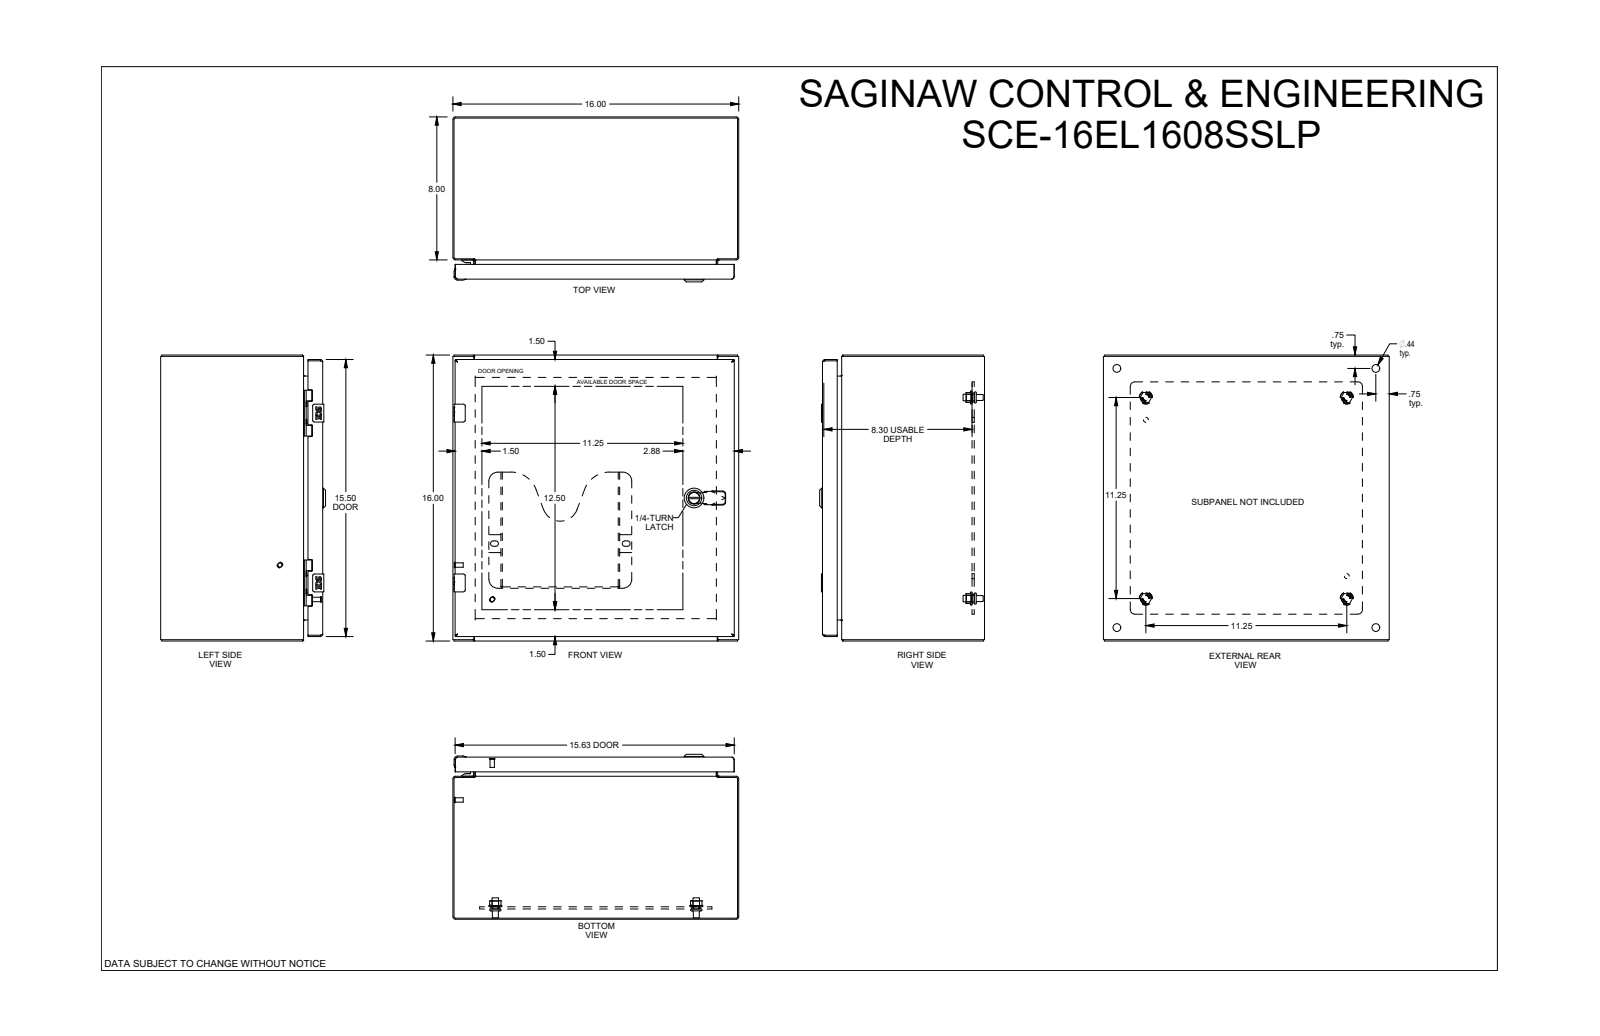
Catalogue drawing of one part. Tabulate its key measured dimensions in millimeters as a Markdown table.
| quantity | value |
| --- | --- |
| part name | SCE-16EL1608LP |
| STEP written by | SolidWorks 2019 (AUTOMOTIVE_DESIGN) |
| units | millimeters |
| bodies | 42 solids, 2221 faces (1015 planar, 558 cylindrical, 648 other) |
| overall size | 406.4 × 406.4 × 234.4 |
| volume | 1 975 000 mm³ |
| surface area | 1 907 000 mm² |
| round holes (diameter × count) | 4.4 × 4, 5.2 × 4, 6.2 × 4, 6.8 × 4, 9.3 × 4, 9.5 × 4, 11.1 × 4, 12.7 × 4, 1 × 2, 4.8 × 2, 5.5 × 2, 6.4 × 2 |
| round bosses / shafts (diameter × count) | 4.3 × 6, 9.3 × 4, 8.4 × 4, 6.4 × 4, 6.3 × 4, 6.1 × 4, 5 × 3, 14.3 × 2 |
| partial cylindrical surfaces (radius × count) | 0.3 × 30, 0.3 × 28, 0.4 × 24, 1 × 17, 1.5 × 13, 0.5 × 12, 0.7 × 12, 2.5 × 12 |
| main face-to-face distances | 1.9, 1.9, 1.5, 404.5, 404.5, 406.4, 230.5, 228.5, 228.9, 227 |
| hole center spacings | 329.6, 25, 241.3, 0.5, 12.5, 12.5, 58.4, 76 |
